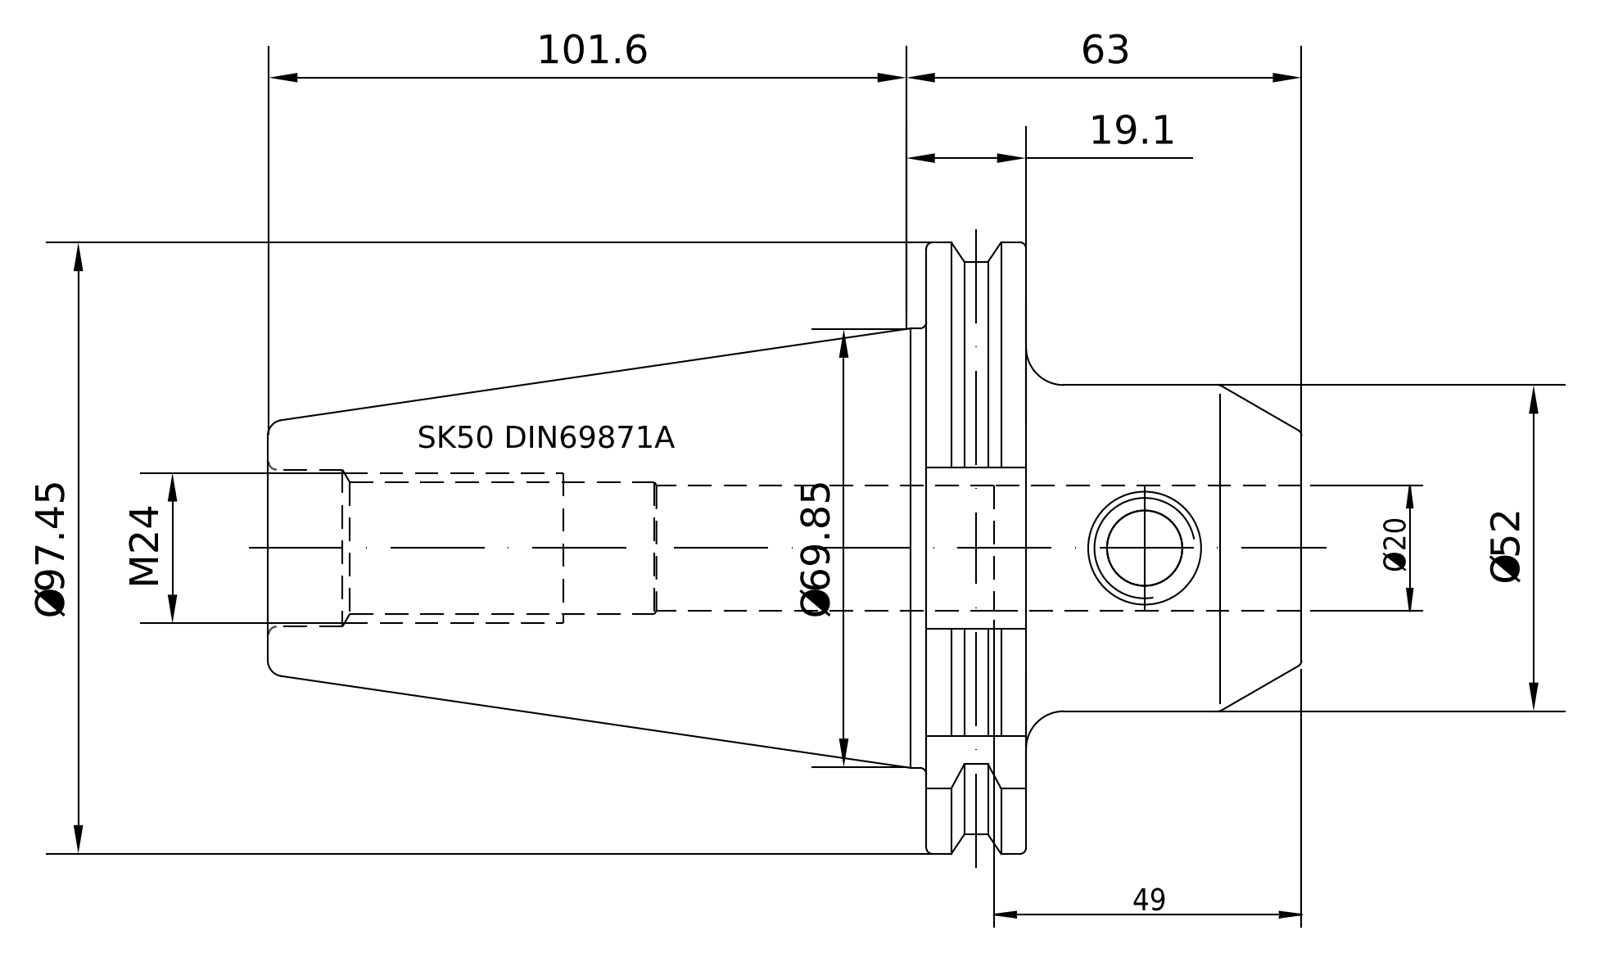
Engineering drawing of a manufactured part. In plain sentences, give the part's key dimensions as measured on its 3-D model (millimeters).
The part is named "50-300-20". Its 3-D file was written by "PRO/ENGINEER BY PARAMETRIC TECHNOLOGY CORPORATION, 2010430 (CONFIG_CONTROL_DESIGN)". It is 1 solid with 103 faces: 21 planar, 32 cylindrical and 50 other. Overall it measures 164.6 by 97.47 by 94 millimeters. Its volume is 405 422 cubic millimeters and its surface area 53 351 square millimeters. Round holes: 1 of diameter 14, 1 of diameter 16, 1 of diameter 20, 1 of diameter 20.75, 1 of diameter 25.01, 1 of diameter 25.7. Round bosses or shafts: 1 of diameter 91, 1 of diameter 69.15, 1 of diameter 52, 1 of diameter 24.01. Partial cylindrical surfaces (rounded edges, fillets, slot ends): 5 of radius 1.75, 1 of radius 48.74. The main face-to-face distances are 15.85, 59.8, 43.95, 104.8, 120.65, 164.6, 72.8, 104.5, 16.15, 60.1.
